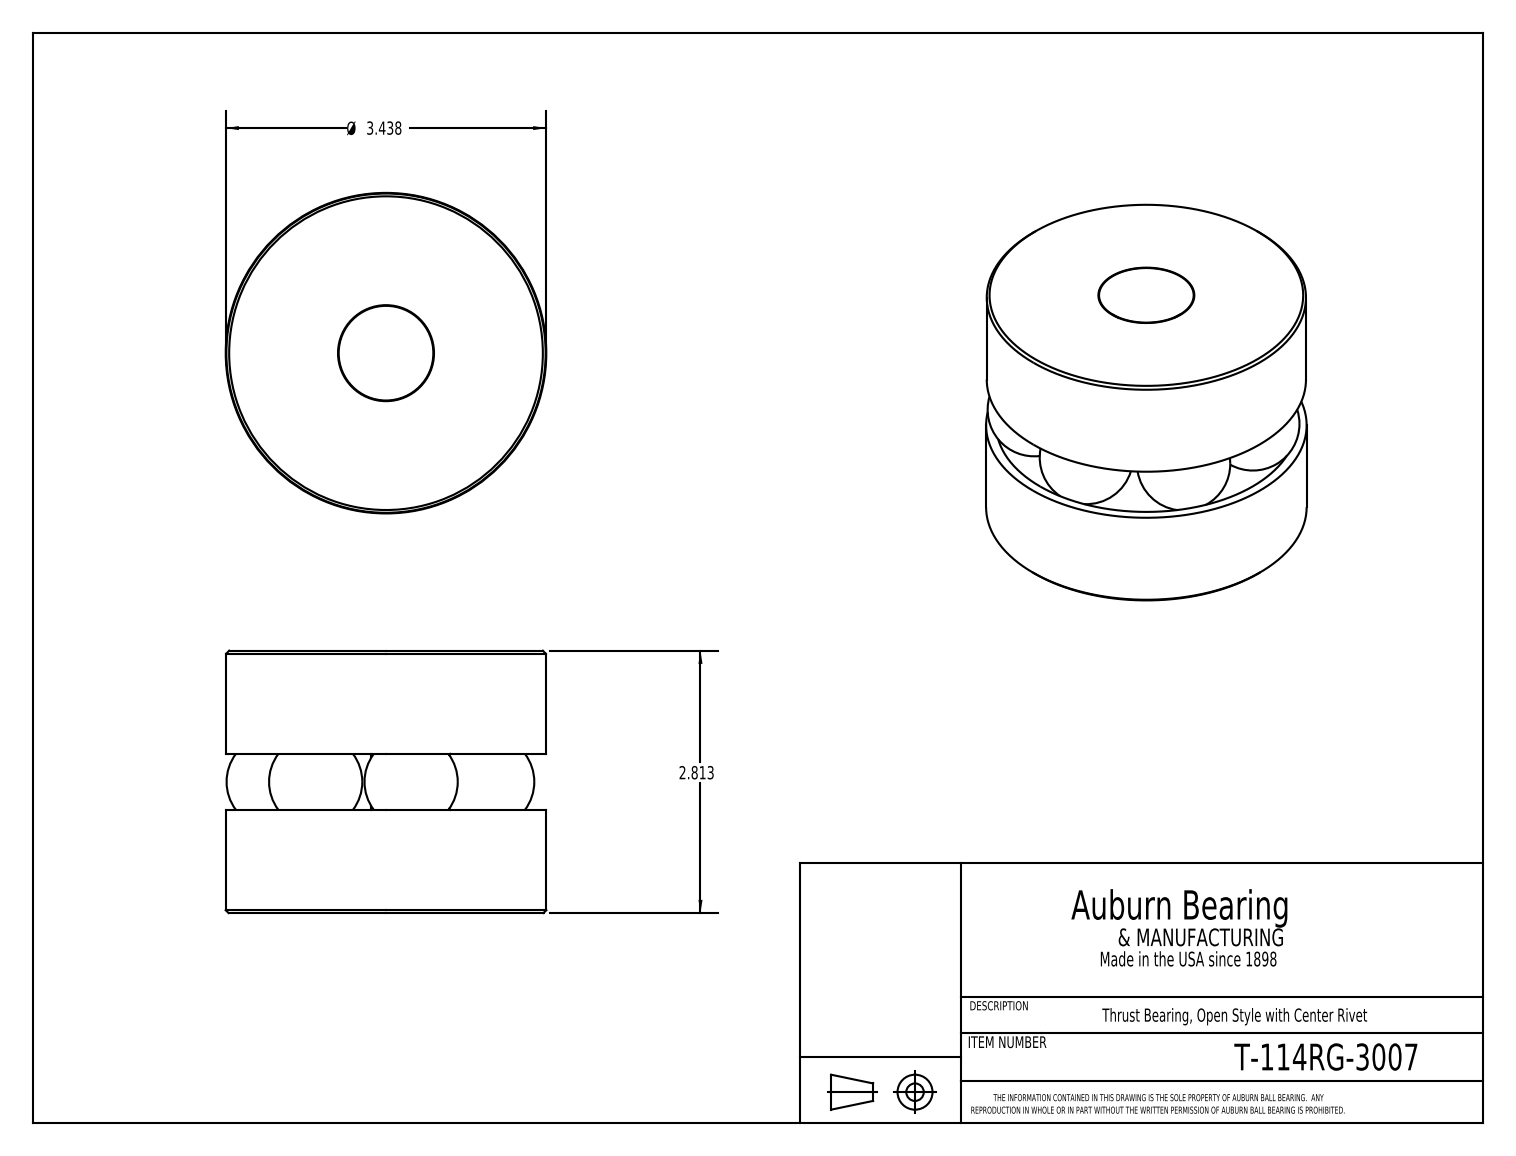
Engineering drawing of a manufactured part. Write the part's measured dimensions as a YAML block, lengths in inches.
part_name: "T-114RG_T-114RG-3007"
step_written_by: "SolidWorks 2016 (CONFIG_CONTROL_DESIGN)"
units: inches
bodies: {solids: 10, faces: 28, planar: 8, cylindrical: 5, other: 15}
overall_size: [3.438, 3.438, 2.813]
volume: 22.44
surface_area: 91.96
round_holes:
  - {diameter: 0.322, count: 1}
round_bosses_or_shafts:
  - {diameter: 3.438, count: 1}
  - {diameter: 3.424, count: 1}
  - {diameter: 0.312, count: 1}
face_to_face_distances: [2.813, 1.107, 1.706, 1.707, 0.6, 1.106]
